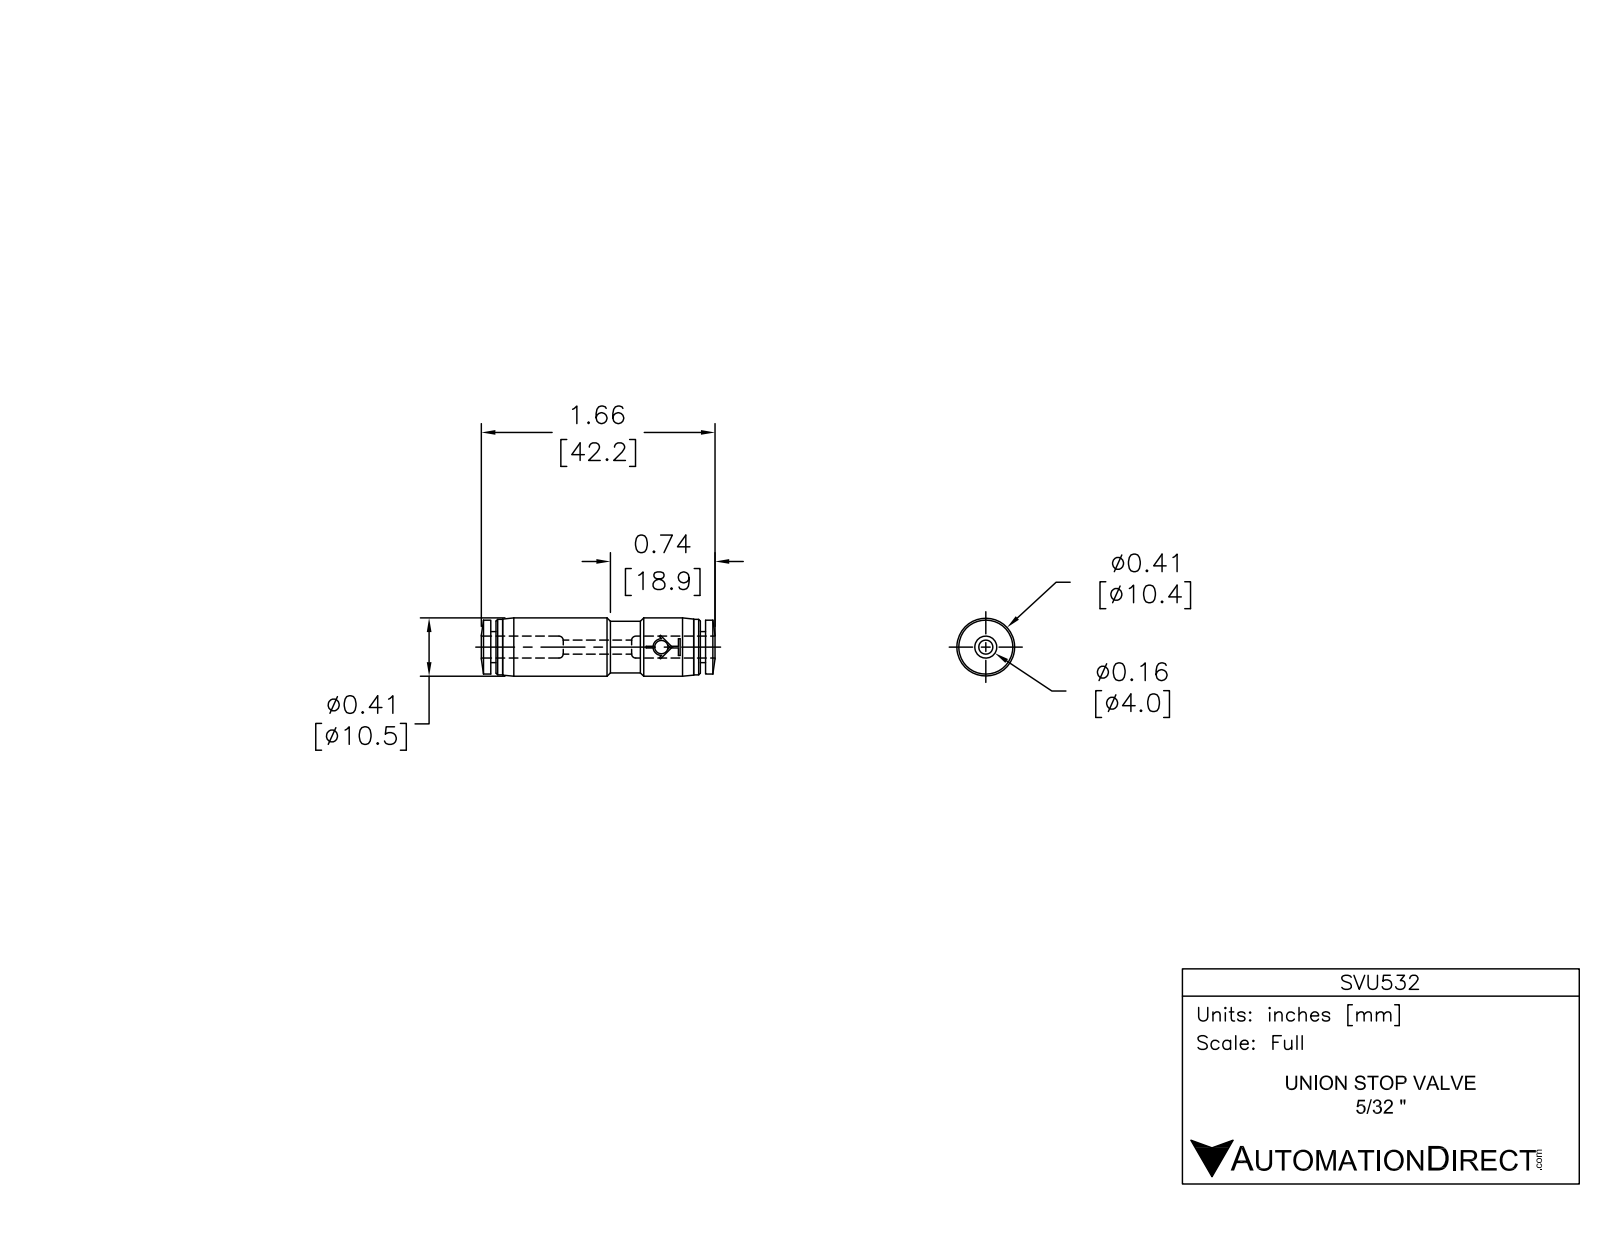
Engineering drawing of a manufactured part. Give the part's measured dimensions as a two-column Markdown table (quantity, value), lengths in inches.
| quantity | value |
| --- | --- |
| part name | SVU532 |
| STEP written by | SolidWorks 2015 (AUTOMOTIVE_DESIGN) |
| units | inches |
| bodies | 1 solid, 82 faces (24 planar, 30 cylindrical, 28 other) |
| overall size | 1.657 × 0.417 × 0.413 |
| volume | 0.17 in³ |
| surface area | 3.37 in² |
| round holes (diameter × count) | 0.094 × 1, 0.122 × 1, 0.169 × 1 |
| round bosses / shafts (diameter × count) | 0.413 × 1, 0.394 × 1, 0.388 × 1, 0.366 × 1, 0.22 × 1 |
| partial cylindrical surfaces (radius × count) | 0.059 × 1, 0.211 × 1 |
| main face-to-face distances | 0.037, 1.486, 1.524, 1.449, 0.52, 1.004, 0.482, 0.967, 0.484, 0.085 |
